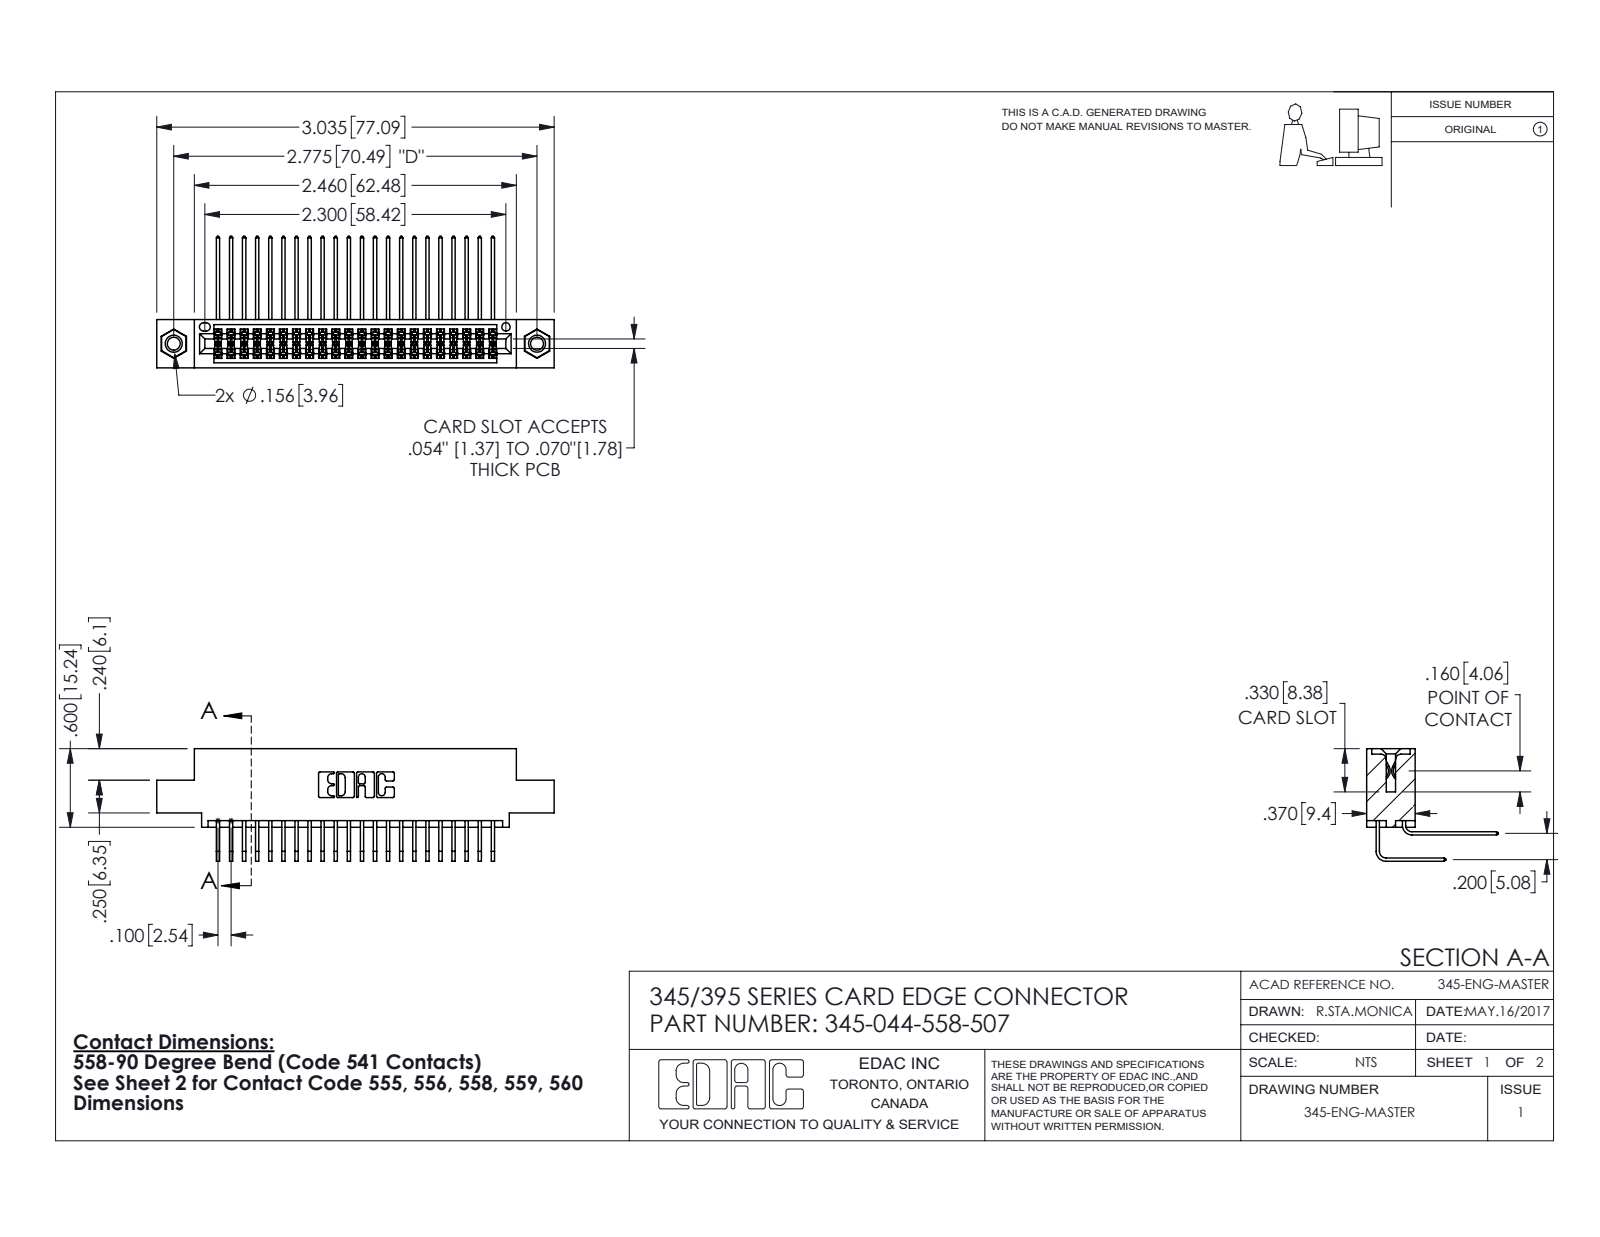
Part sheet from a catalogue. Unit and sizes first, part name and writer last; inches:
Units: inches
Overall size (bounding box): 3.035 × 1.005 × 0.859
Round holes (diameter × count): ⌀0.098 ×2, ⌀0.125 ×2, ⌀0.156 ×2, ⌀0.064 ×1
Round bosses / shafts (diameter × count): ⌀0.155 ×2
Partial cylindrical surfaces — rounded edges, fillets, slot ends (radius × count): R0.006 ×88, R0.01 ×22, R0.007 ×6, R0.031 ×6, R0.026 ×3, R0.014 ×2, R0.019 ×2, R0.022 ×2
Main face-to-face distances: 0.072, 0.298, 0.2, 0.37, 0.098, 0.272, 0.025, 0.225, 0.025, 0.175
Hole centre spacings: 0.27, 2.541, 2.775
Volume: 0.456 in³ · Surface area: 18.55 in²
Bodies: 47 solids, 2478 faces (1656 planar, 806 cylindrical, 16 other)
Part name (STEP PRODUCT): 345 Part_0.110 Offset - 0.156 Dia-TI; 345-292-001_558 Tail - 2; 345-044-558-507; 345-250-001_345-250-005-103 (+1 more)
STEP written by: SolidWorks 2016 (CONFIG_CONTROL_DESIGN)
